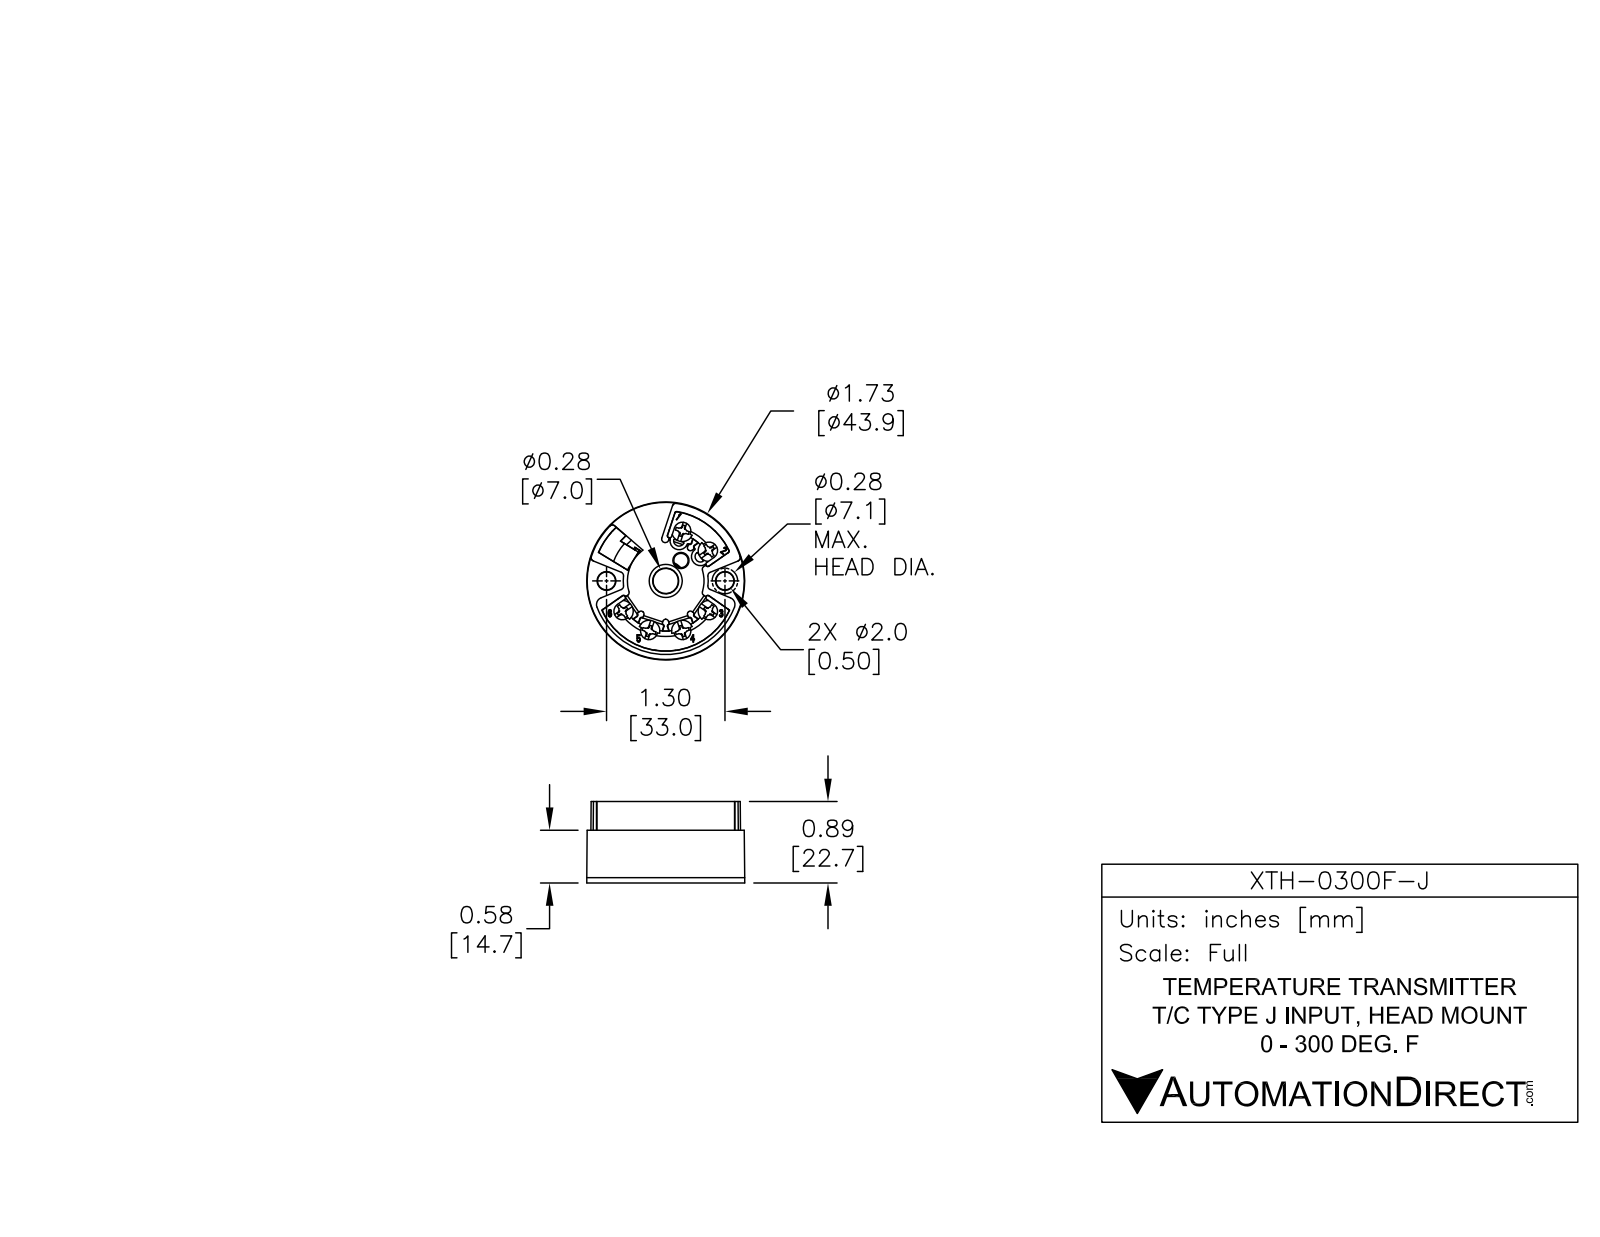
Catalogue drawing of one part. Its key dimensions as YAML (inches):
part_name: "XTH-0100F-J"
step_written_by: "SolidWorks 2017 (AUTOMOTIVE_DESIGN)"
units: inches
bodies: {solids: 1, faces: 1228, planar: 652, cylindrical: 318, other: 258}
overall_size: [1.732, 1.732, 0.894]
volume: 0.586
surface_area: 27.13
round_holes:
  - {diameter: 0.126, count: 6}
  - {diameter: 0.059, count: 4}
  - {diameter: 0.213, count: 2}
  - {diameter: 0.248, count: 2}
  - {diameter: 0.177, count: 1}
  - {diameter: 0.283, count: 1}
  - {diameter: 1.614, count: 1}
round_bosses_or_shafts:
  - {diameter: 0.236, count: 6}
  - {diameter: 0.118, count: 6}
  - {diameter: 0.055, count: 4}
  - {diameter: 0.295, count: 2}
  - {diameter: 0.252, count: 2}
  - {diameter: 1.732, count: 1}
  - {diameter: 0.422, count: 1}
  - {diameter: 0.343, count: 1}
partial_cylinders:
  - {radius: 0.02, count: 31}
  - {radius: 0.008, count: 30}
  - {radius: 0.016, count: 29}
  - {radius: 0.018, count: 12}
  - {radius: 0.031, count: 11}
  - {radius: 0.039, count: 11}
  - {radius: 0.012, count: 7}
  - {radius: 0.093, count: 6}
face_to_face_distances: [0.039, 0.539, 0.5, 0.579, 0.315, 0.854, 0.354, 0.894, 0.031, 0.028]
hole_center_spacings: [0.579, 0.1, 0.364, 0.375, 0.721, 0.997, 1.099, 1.172]
